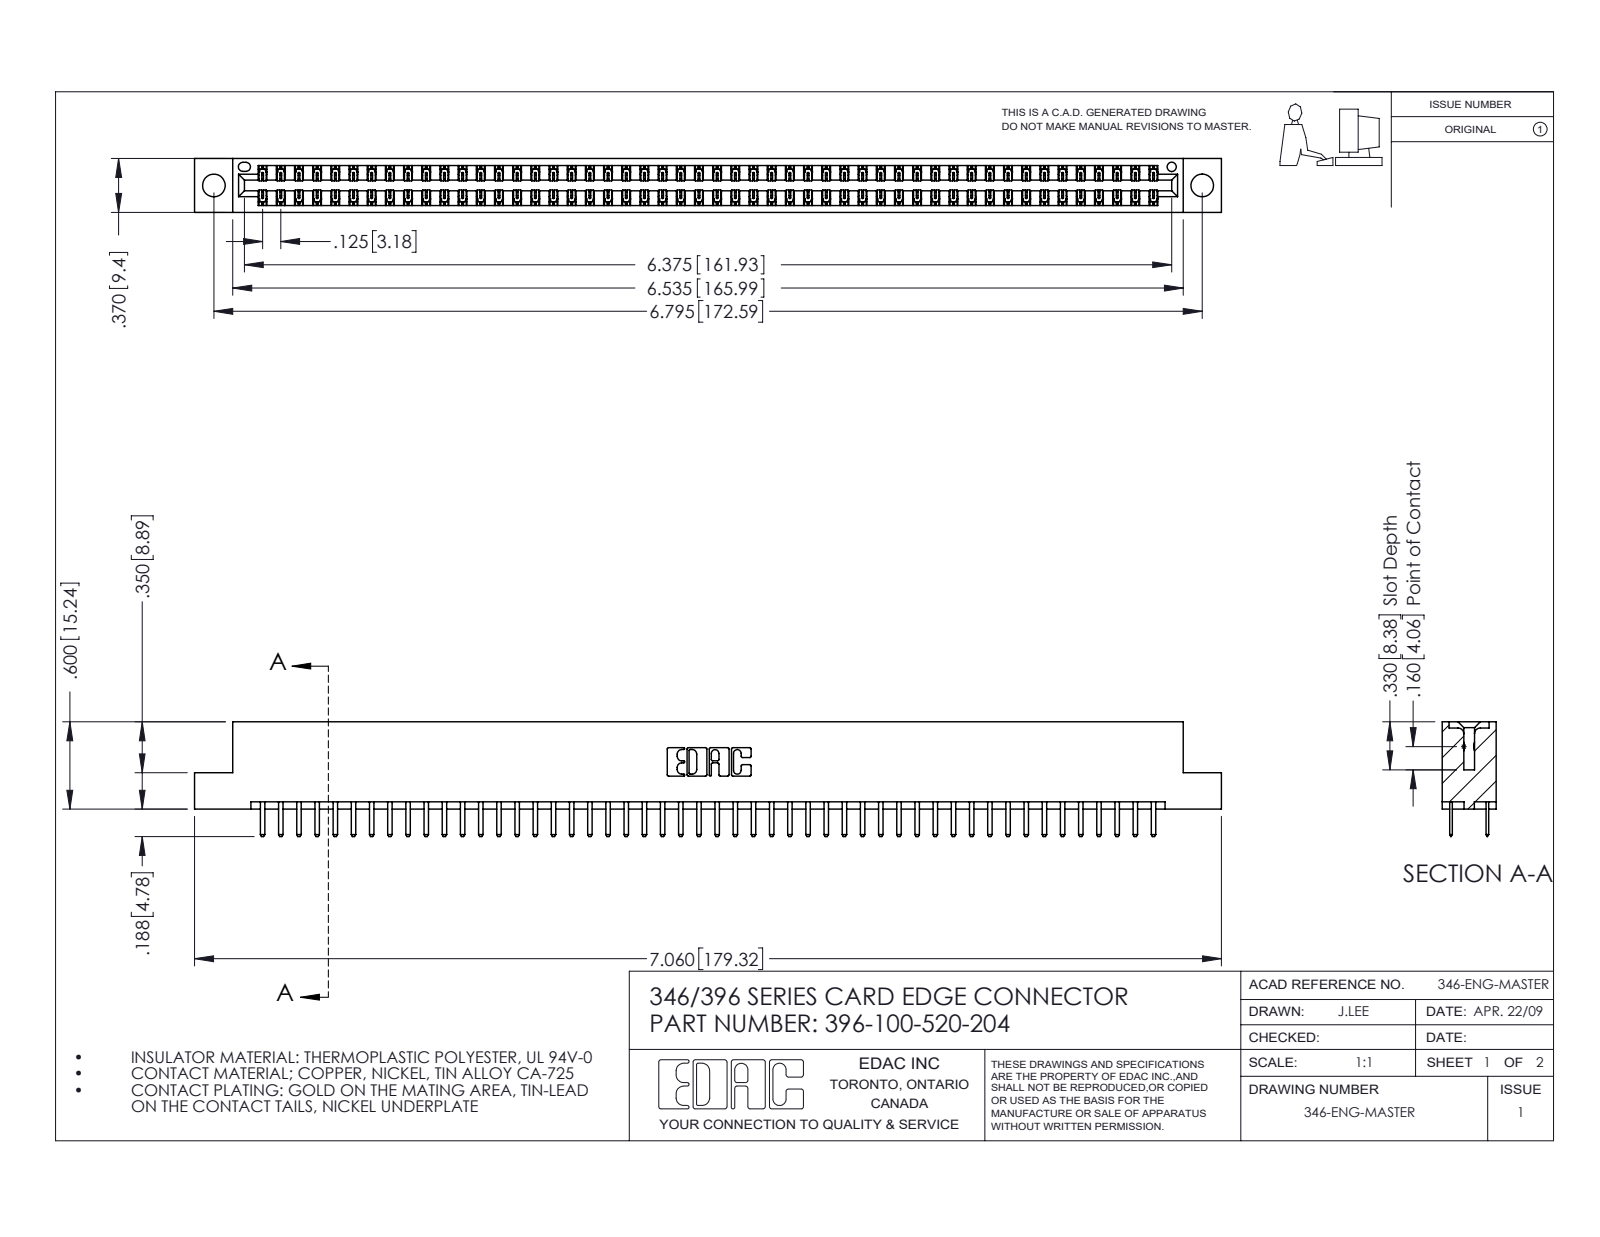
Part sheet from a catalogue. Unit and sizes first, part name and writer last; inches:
Units: inches
Overall size (bounding box): 7.06 × 0.788 × 0.37
Round holes (diameter × count): ⌀0.156 ×2, ⌀0.064 ×1
Partial cylindrical surfaces — rounded edges, fillets, slot ends (radius × count): R0.006 ×150, R0.01 ×104, R0.01 ×22, R0.007 ×6, R0.031 ×6, R0.026 ×3, R0.014 ×2, R0.022 ×2
Main face-to-face distances: 0.048, 0.322, 0.25, 0.37, 0.275, 0.072, 0.298, 0.025, 0.148, 0.222
Hole centre spacings: 0.246, 6.586, 6.795
Volume: 1.063 in³ · Surface area: 36.85 in²
Bodies: 101 solids, 5722 faces (3776 planar, 1946 cylindrical, 0 other)
Part name (STEP PRODUCT): 345-292-001_345-293-120; 396-100-520-204; 346 Part_Flush Mounting Lugs - 0.156 Dia-TH
STEP written by: SolidWorks 2016 (CONFIG_CONTROL_DESIGN)
